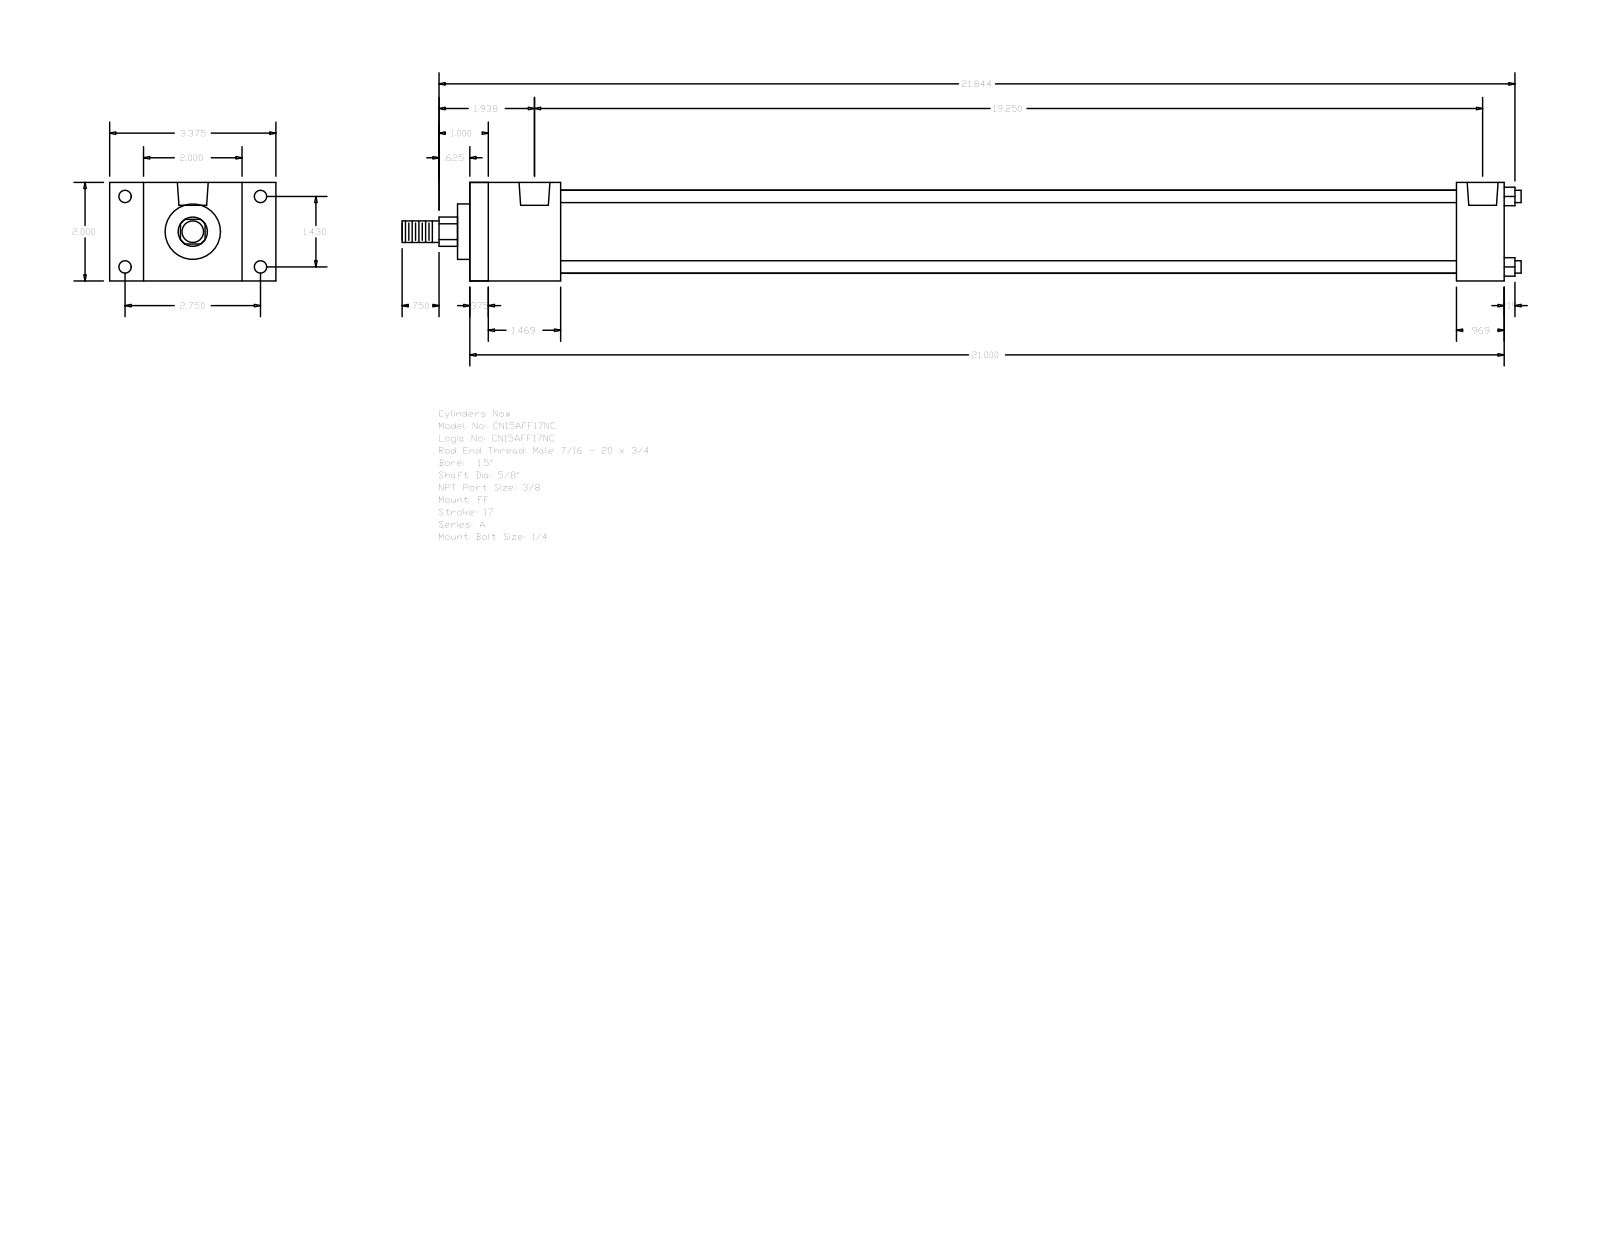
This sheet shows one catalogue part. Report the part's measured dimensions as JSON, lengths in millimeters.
{"part_name": "A_FF__0150_0.625", "step_written_by": "GSSL Pune (CONFIG_CONTROL_DESIGN)", "units": "millimeters", "bodies": {"solids": 0, "faces": 92, "planar": 64, "cylindrical": 28, "other": 0}, "overall_size": [577.06, 85.72, 50.8], "round_holes": [[5.56, 4], [6.35, 4], [15.93, 2]], "round_bosses_or_shafts": [[6.35, 4], [42.93, 1], [28.57, 1], [15.88, 1], [11.11, 1]], "partial_cylinders_radius": [[7.54, 1]], "face_to_face_distances": [50.8, 533.39, 9.52, 523.87, 46.83, 508.79, 37.31, 499.27, 461.96, 486.56], "hole_center_spacings": [3.97, 36.32, 69.84, 78.72, 481.01, 484.98, 488.95]}
